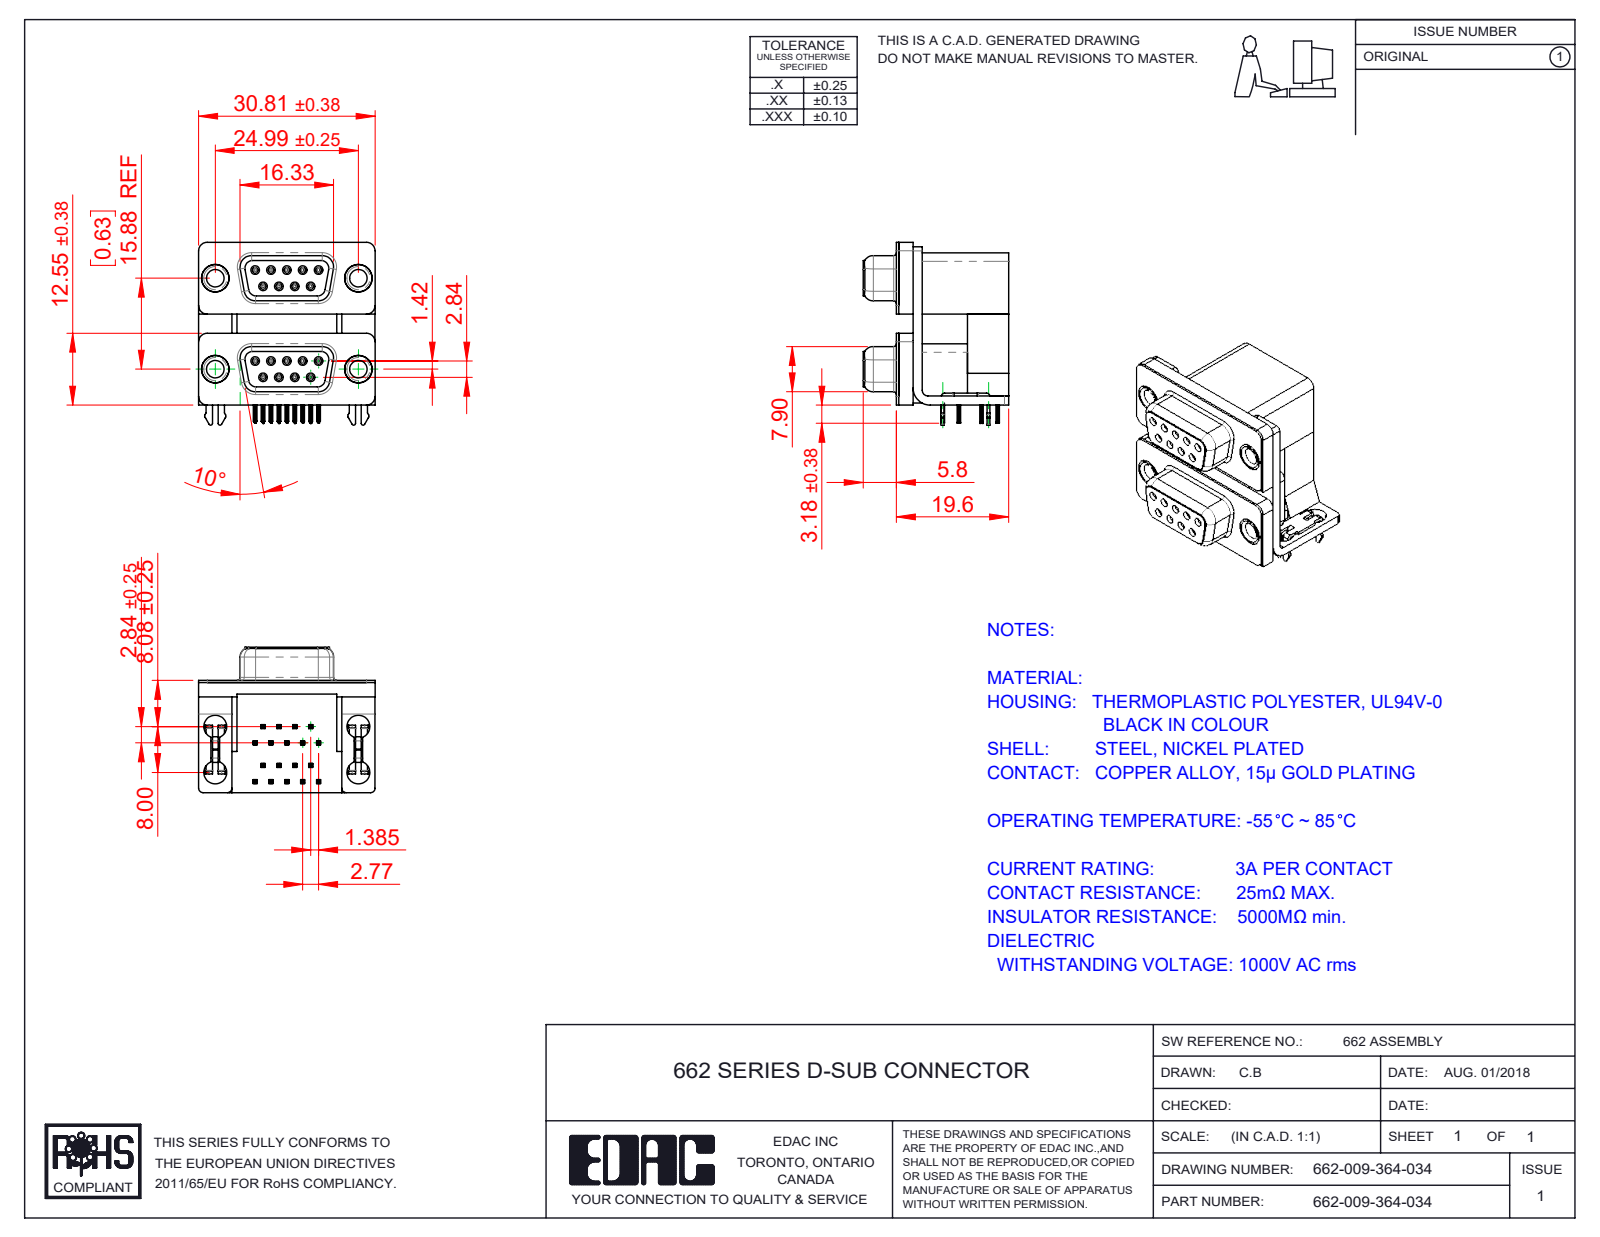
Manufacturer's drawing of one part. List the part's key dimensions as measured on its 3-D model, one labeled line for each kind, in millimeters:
Part name (STEP PRODUCT): 662 2 Prong Board Lock_3; 662 Thru Hole Rivet; 662 Housing Upper_09 Contacts L; 662 Shell_09 Contacts (+8 more)
STEP written by: SolidWorks 2020 (CONFIG_CONTROL_DESIGN)
Units: millimetres
Bodies: 31 solids, 3178 faces (1476 planar, 810 cylindrical, 892 other)
Overall size (bounding box): 31.93 × 30.81 × 25.4
Volume: 10 829 mm³ · Surface area: 12 995 mm²
Round holes (diameter × count): ⌀0.8 ×18, ⌀0.9 ×18, ⌀4 ×8, ⌀3.05 ×4, ⌀3.5 ×4, ⌀4.8 ×4, ⌀5 ×4
Round bosses / shafts (diameter × count): ⌀1.2 ×18, ⌀4.9 ×4, ⌀4.75 ×4, ⌀3.85 ×4
Partial cylindrical surfaces — rounded edges, fillets, slot ends (radius × count): R0.1 ×146, R0.15 ×72, R0.35 ×36, R0.34 ×18, R1.35 ×18, R0.5 ×12, R1.5 ×12, R0.25 ×10
Main face-to-face distances: 2.5, 0.4, 16.7, 19.2, 2.9, 19.6, 15.88, 7.2, 9.5, 12
Hole centre spacings: 2.77, 5.54, 3.16, 16.12, 8.31, 15.88, 16.82, 5.03
